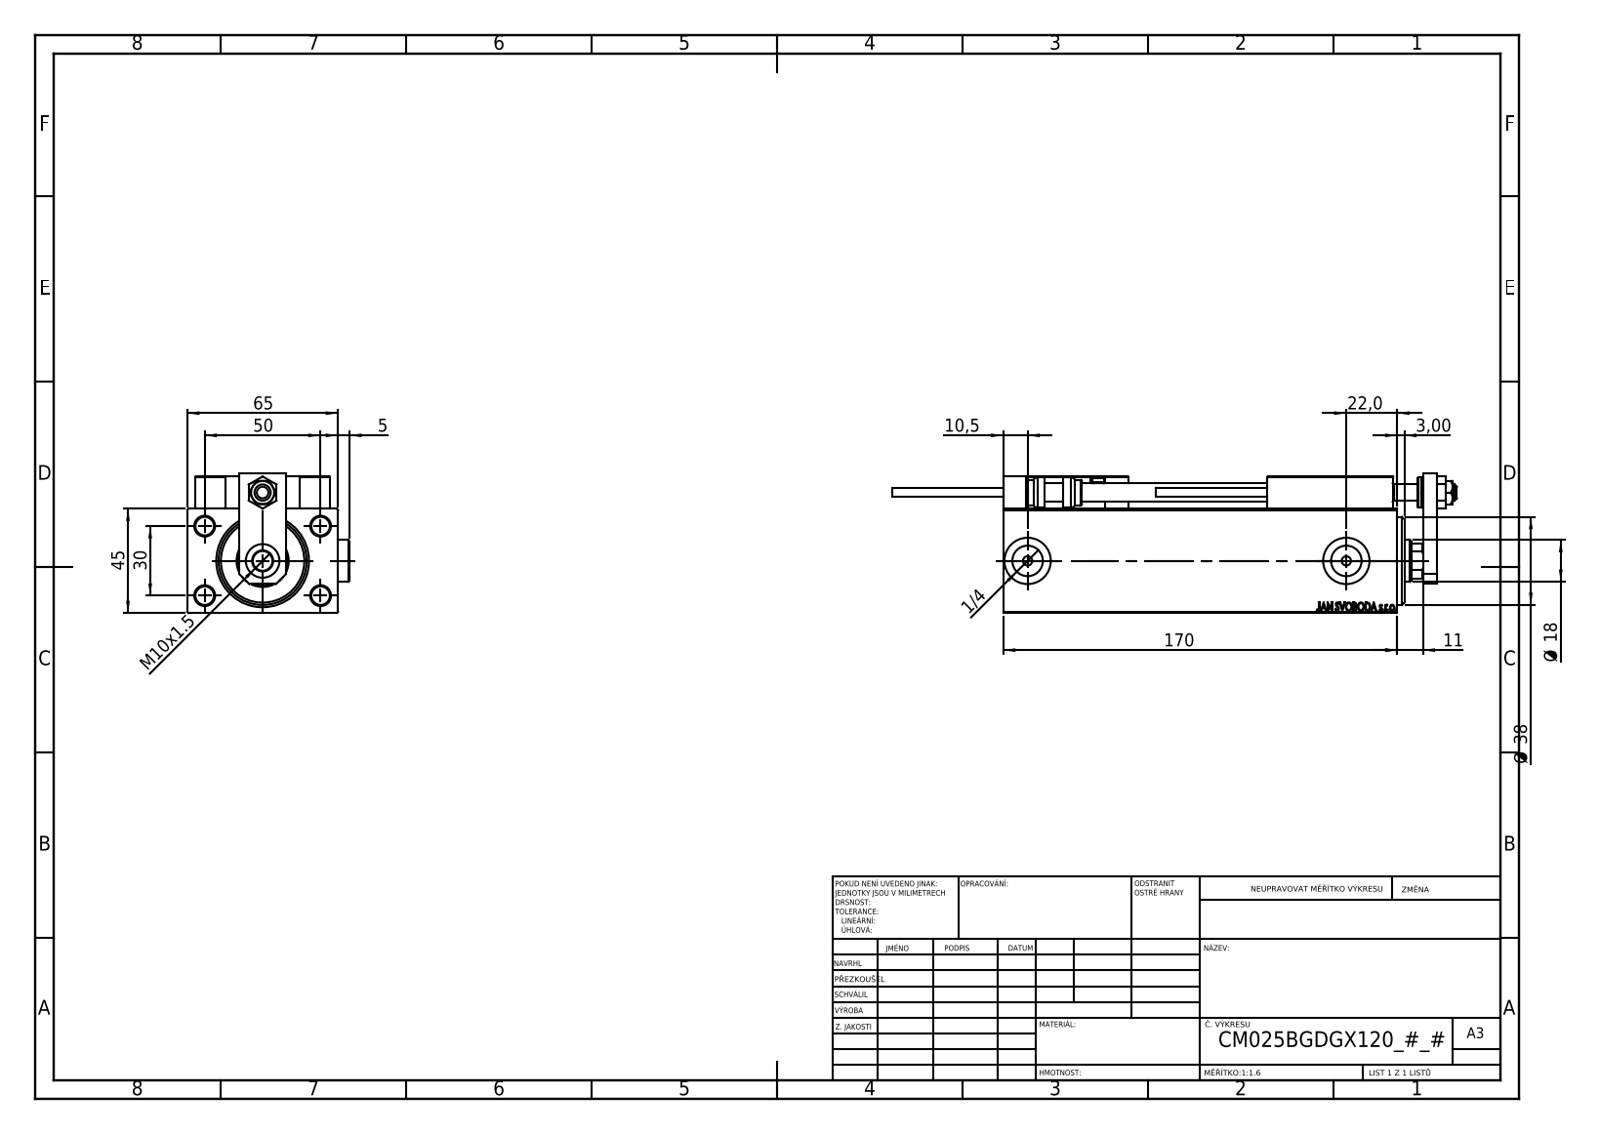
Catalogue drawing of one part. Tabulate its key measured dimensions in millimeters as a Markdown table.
| quantity | value |
| --- | --- |
| part name | SWITCH DIM B,W; Block; NUT_D10; KONCOVKA (+8 more) |
| STEP written by | SolidWorks 2019 (CONFIG_CONTROL_DESIGN) |
| units | millimeters |
| bodies | 26 solids, 1372 faces (595 planar, 200 cylindrical, 577 other) |
| overall size | 243.7 × 69.9 × 60.5 |
| volume | 511 335 mm³ |
| surface area | 105 125 mm² |
| round holes (diameter × count) | 8 × 9, 4 × 6, 3.2 × 4, 5 × 2, 13.16 × 2, 20 × 2, 7 × 1, 8.5 × 1, 14.5 × 1, 18 × 1, 21.5 × 1, 22.5 × 1 |
| round bosses / shafts (diameter × count) | 18 × 2, 5 × 2, 3.8 × 2, 13 × 1, 11 × 1 |
| partial cylindrical surfaces (radius × count) | 0.3 × 30, 3 × 2, 8.5 × 1 |
| main face-to-face distances | 45, 65, 14, 6, 59, 5, 13, 3.5, 181, 19 |
| hole center spacings | 29.15, 11.37, 20, 28.9, 29.59, 29.69, 30, 36.06 |
